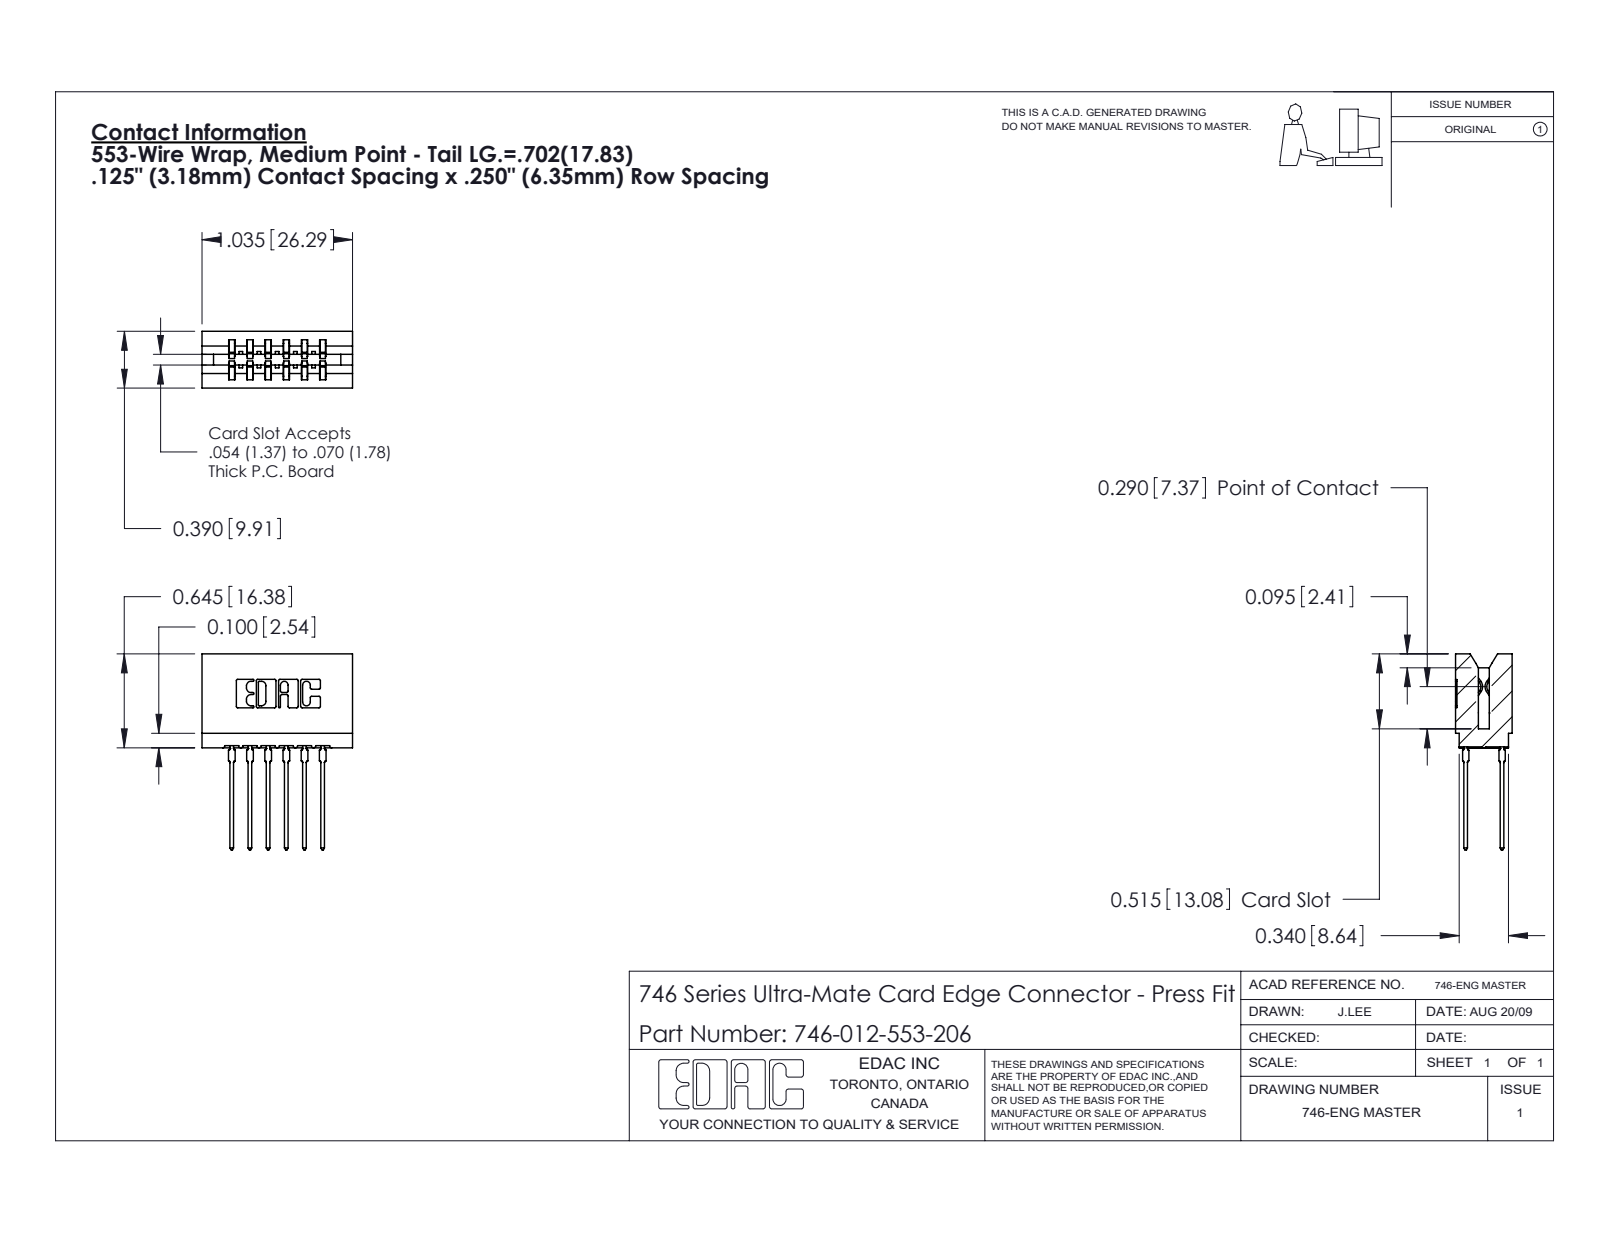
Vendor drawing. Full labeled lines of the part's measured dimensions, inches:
Part name (STEP PRODUCT): 746 Part_.515 Slot Depth - 06; 746-012-553-206; 746-292-001_553
STEP written by: SolidWorks 2020 (CONFIG_CONTROL_DESIGN)
Units: inches
Bodies: 13 solids, 1172 faces (608 planar, 252 cylindrical, 312 other)
Overall size (bounding box): 1.346 × 1.035 × 0.39
Volume: 0.188 in³ · Surface area: 6.954 in²
Partial cylindrical surfaces — rounded edges, fillets, slot ends (radius × count): R0.021 ×24, R0.01 ×22, R0.005 ×8, R0.011 ×8, R0.015 ×7, R0.007 ×6, R0.031 ×6, R0.026 ×3
Main face-to-face distances: 0.25, 0.057, 0.125, 0.333, 0.042, 0.083, 0.125, 0.025, 0.5, 0.375
